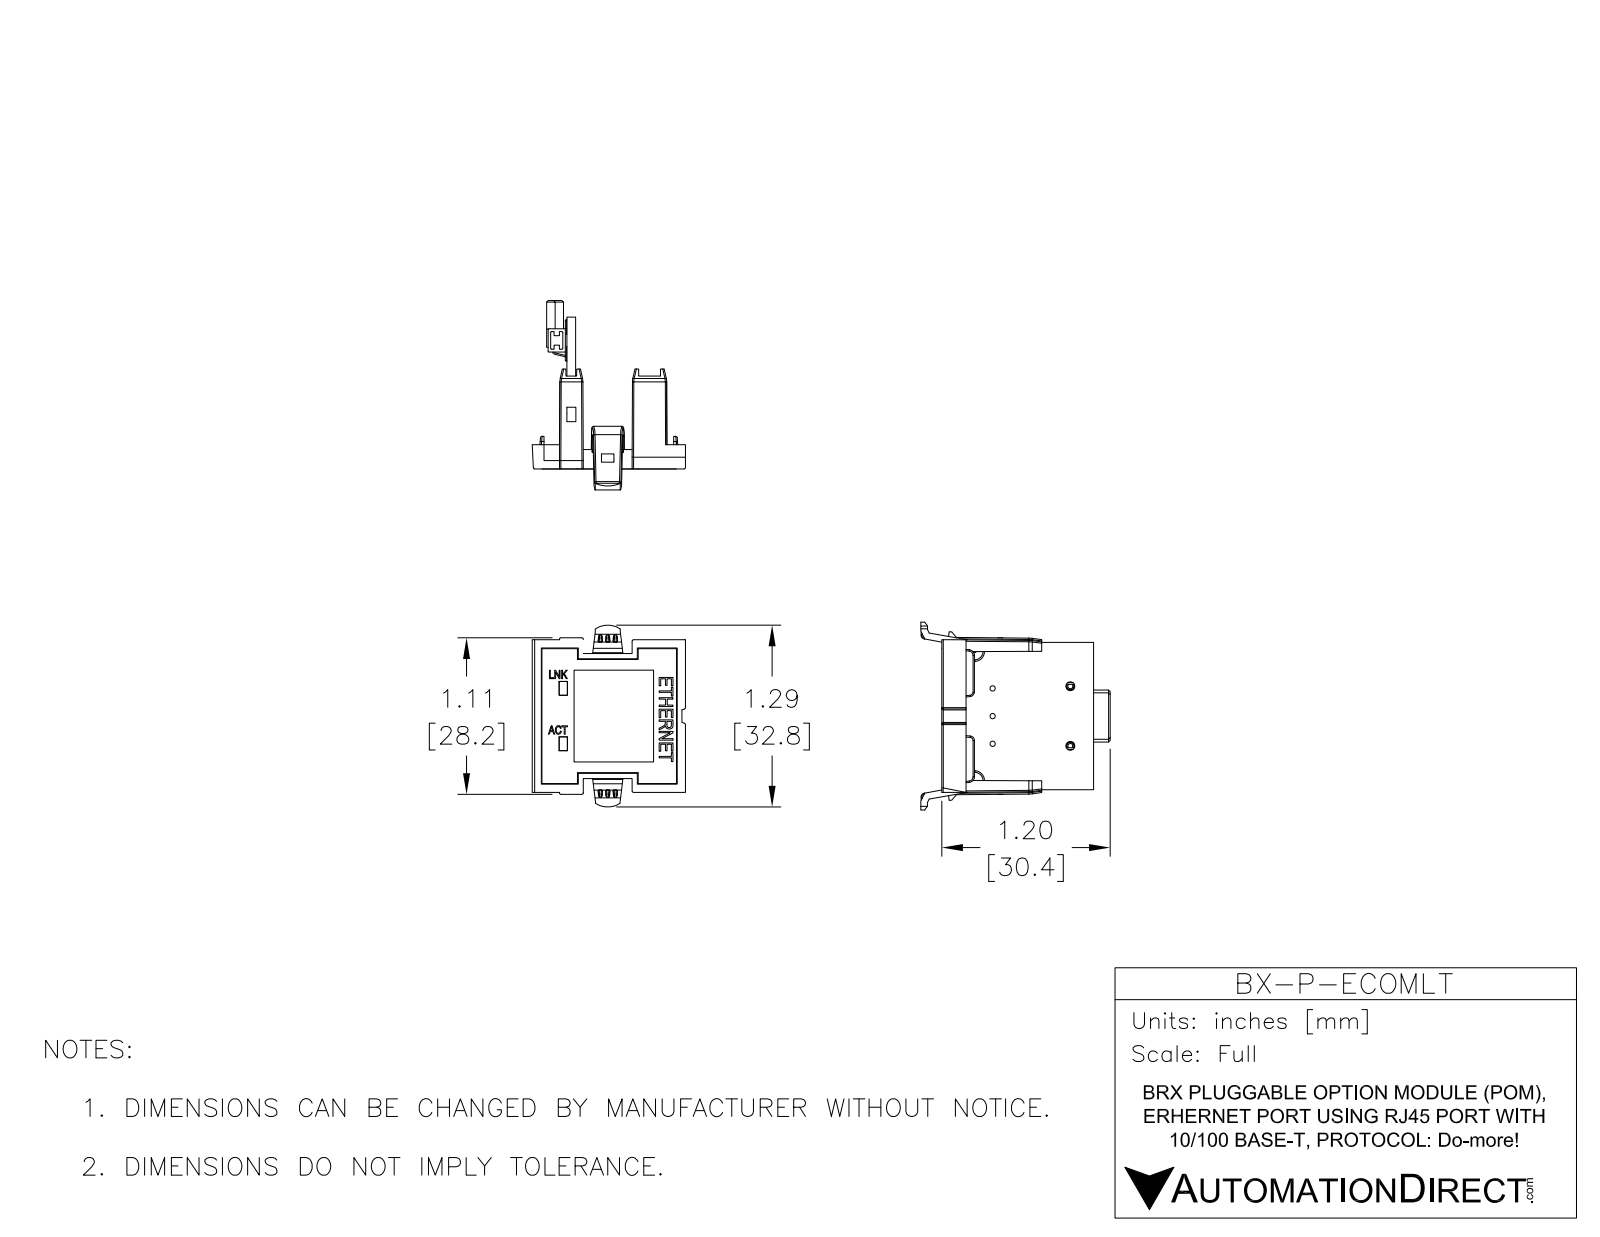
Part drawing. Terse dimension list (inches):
name: BX-P-ECOMLT
written by: SolidWorks 2016 (AUTOMOTIVE_DESIGN)
unit: in
bodies: 50 solids, 1836 faces (1552 planar, 237 cylindrical, 47 other)
size: 1.363 × 1.334 × 1.084
volume: 0.39 in³; area: 14.62 in²
holes: 3× ⌀0.037, 2× ⌀0.063
bosses: 2× ⌀0.118
rounds: 47× R0.008, 40× R0.004, 10× R0.033, 8× R0.006, 5× R0.016, 5× R0.049, 4× R0.01, 4× R0.108
face distances: 0.062, 0.61, 0.548, 0.626, 0.066, 0.614, 0.485, 0.423, 0.125, 0.741
hole spacings: 0.552, 0.196, 0.197, 0.393, 0.424, 0.591, 0.592, 0.687
